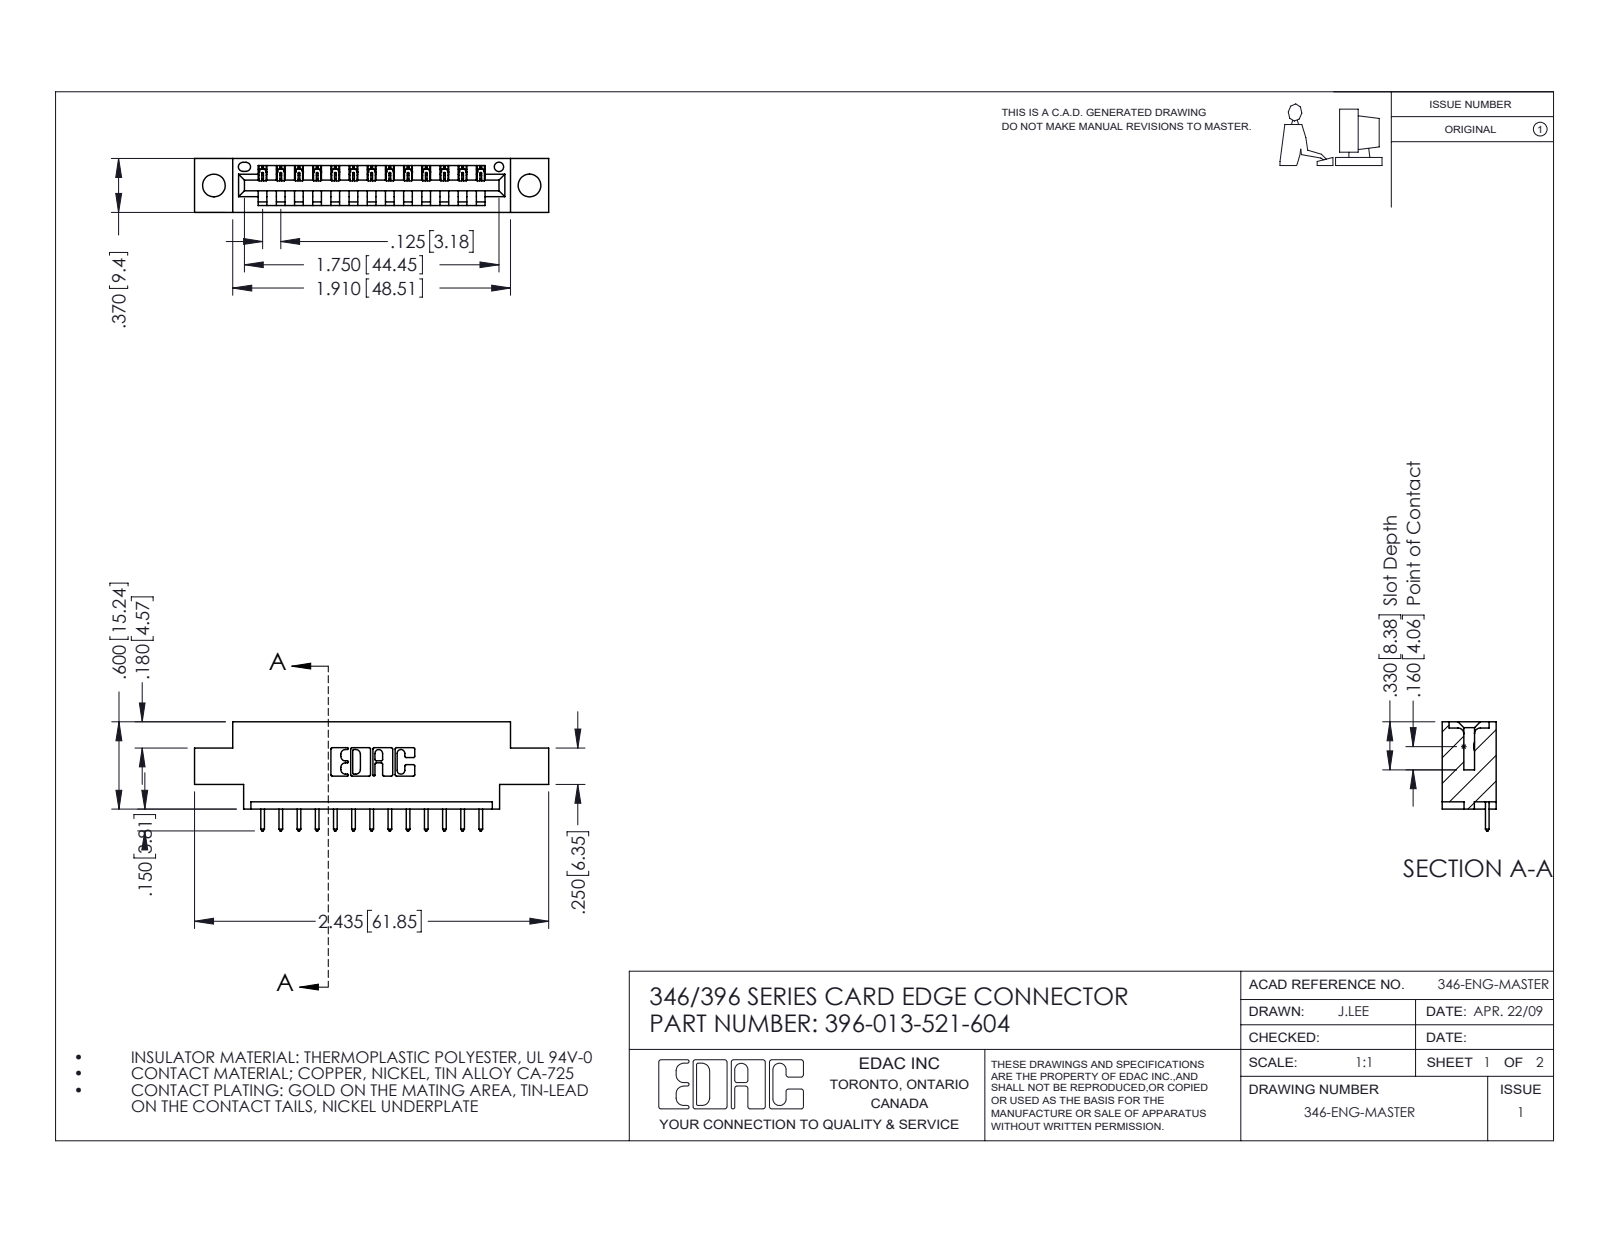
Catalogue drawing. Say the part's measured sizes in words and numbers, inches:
The part is named "345-292-001_345-293-121; 346 Part_0.170 Offset - 0.156 Dia-TH; 396-013-521-604". Its 3-D file was written by "SolidWorks 2016 (CONFIG_CONTROL_DESIGN)". It is 14 solids with 880 faces: 600 planar, 280 cylindrical and 0 other. Overall it measures 2.435 by 0.75 by 0.37 inches. Its volume is 0.332 cubic inches and its surface area 9.774 square inches. Round holes: 2 of diameter 0.156, 1 of diameter 0.064. Partial cylindrical surfaces (rounded edges, fillets, slot ends): 26 of radius 0.006, 26 of radius 0.01, 22 of radius 0.01, 6 of radius 0.007, 6 of radius 0.031, 3 of radius 0.026, 2 of radius 0.031, 2 of radius 0.04. The main face-to-face distances are 0.37, 0.25, 0.048, 0.322, 0.148, 0.072, 0.298, 0.025, 0.222, 0.1. The hole center spacings are 0.246, 1.964, 2.17.
